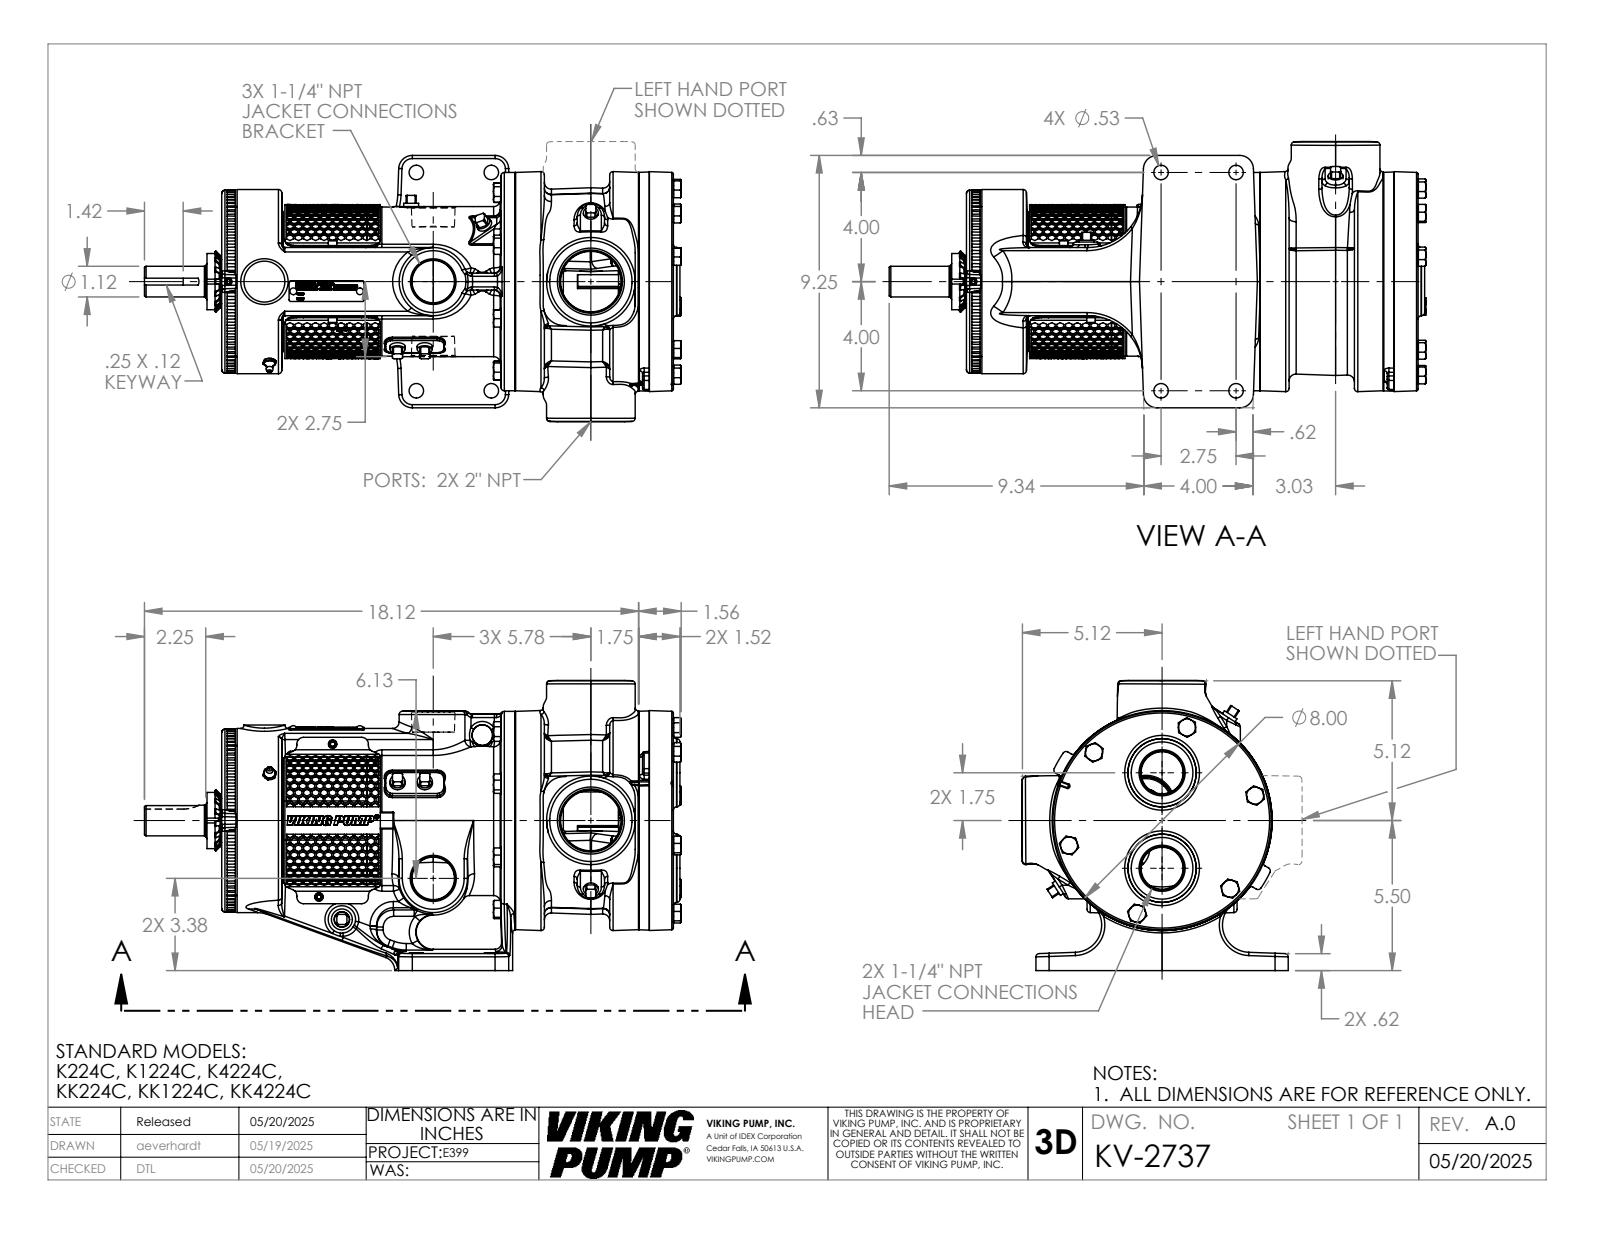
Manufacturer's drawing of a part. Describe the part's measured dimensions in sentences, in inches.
The part is named "KV-2737". Its 3-D file was written by "SolidWorks 2024 (AUTOMOTIVE_DESIGN)". It is 1 solid with 3651 faces: 1235 planar, 416 cylindrical and 2000 other. Overall it measures 19.679 by 10.636 by 9.761 inches. Its volume is 586.3 cubic inches and its surface area 930.6 square inches. Round holes: 8 of diameter 0.78, 6 of diameter 0.197, 6 of diameter 0.25, 4 of diameter 0.531, 2 of diameter 0.159, 2 of diameter 0.313, 1 of diameter 0.257, 1 of diameter 0.453, 1 of diameter 1.38, 1 of diameter 1.387, 1 of diameter 1.624, 1 of diameter 1.698. Round bosses or shafts: 10 of diameter 0.625, 4 of diameter 0.625, 3 of diameter 0.437, 3 of diameter 0.312, 1 of diameter 8, 1 of diameter 6.75, 1 of diameter 5.5, 1 of diameter 5.497. Partial cylindrical surfaces (rounded edges, fillets, slot ends): 38 of radius 0.12, 22 of radius 0.24, 20 of radius 0.03, 16 of radius 0.12, 11 of radius 0.06, 10 of radius 0.5, 8 of radius 0.25, 7 of radius 0.237. The main face-to-face distances are 4.75, 11.245, 5.315, 16.56, 0.5, 4, 0.565, 15.995, 1.5, 0.065. The hole center spacings are 3, 1.03, 1.376, 2.385, 2.909, 3.531, 3.655, 3.799.
